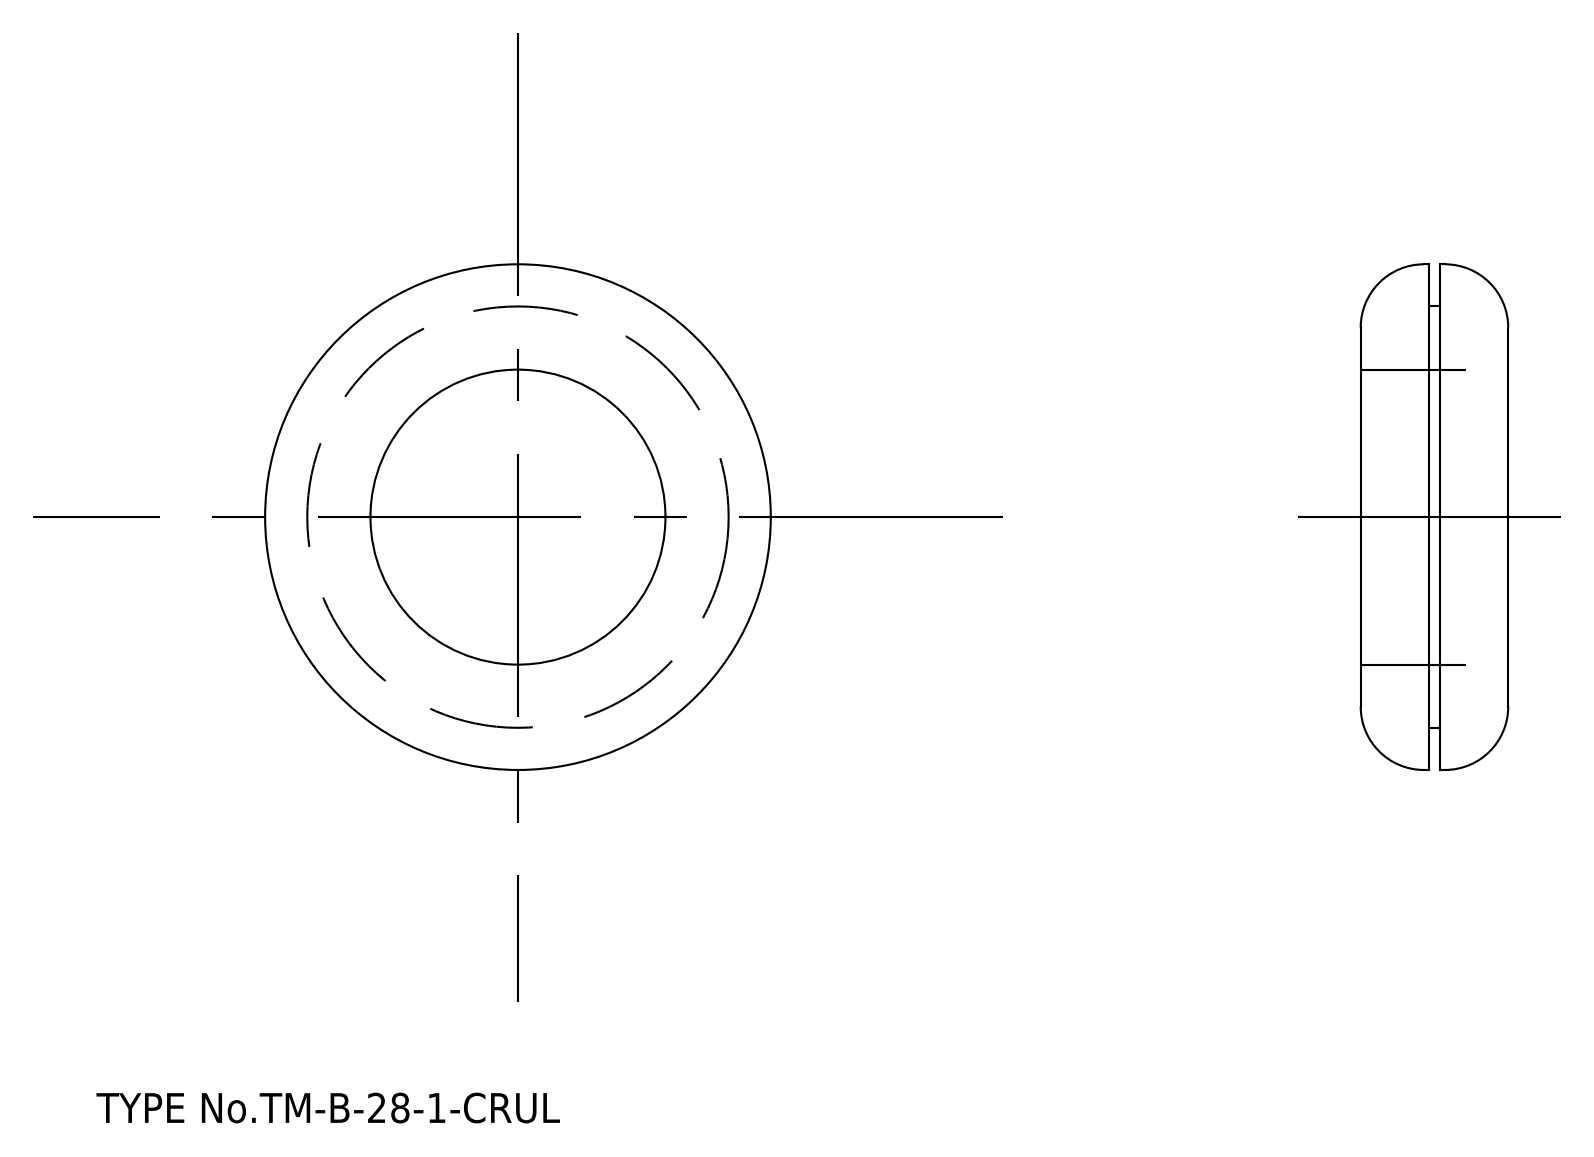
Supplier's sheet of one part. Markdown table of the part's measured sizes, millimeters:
| quantity | value |
| --- | --- |
| STEP written by | spGate 15.6.1 (AUTOMOTIVE_DESIGN) |
| units | millimeters |
| bodies | 1 solid, 16 faces (4 planar, 8 cylindrical, 4 other) |
| overall size | 48 × 48 × 14 |
| volume | 13 971 mm³ |
| surface area | 6 006 mm² |
| round holes (diameter × count) | 28 × 1 |
| round bosses / shafts (diameter × count) | 48 × 1, 40 × 1 |
| main face-to-face distances | 6.5, 7.5, 1, 14 |
